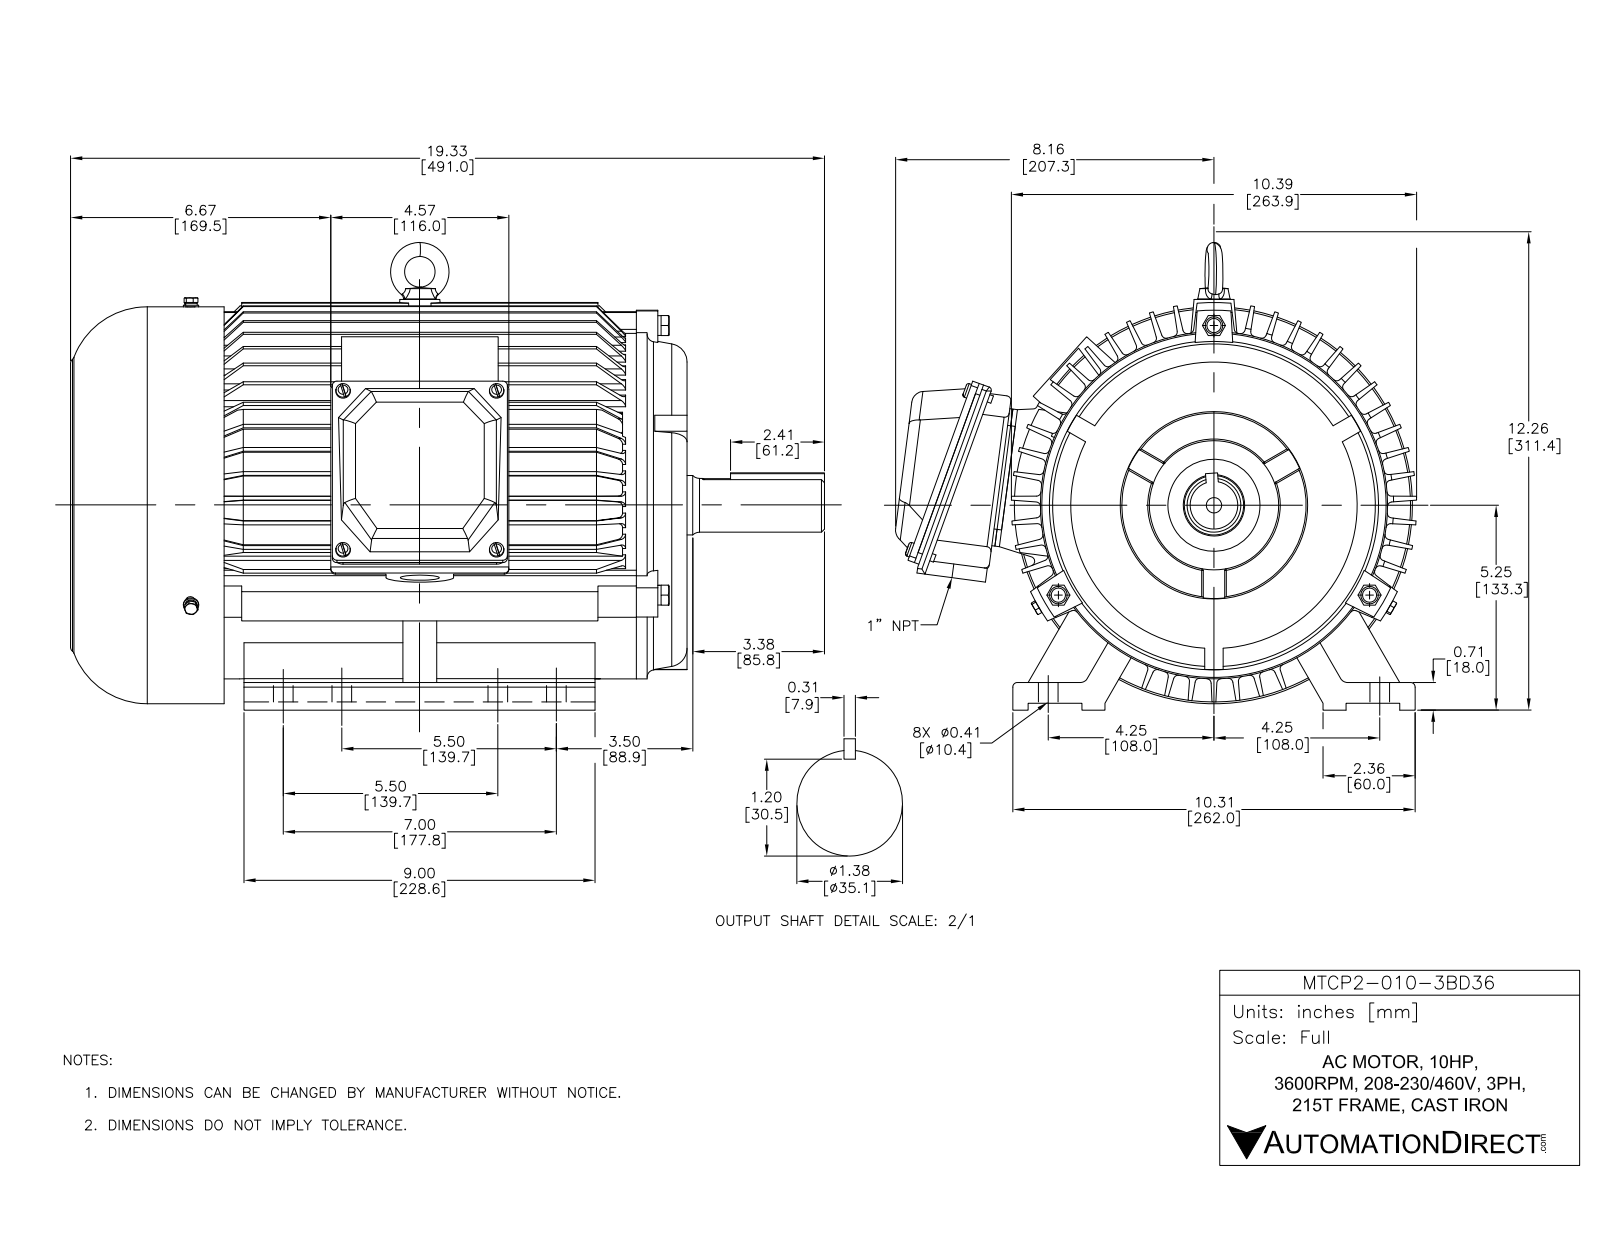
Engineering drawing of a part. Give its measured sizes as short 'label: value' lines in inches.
name: MTCP2-010-3BD18 215T
written by: SolidWorks 2017 (AUTOMOTIVE_DESIGN)
unit: in
bodies: 27 solids, 1887 faces (1094 planar, 527 cylindrical, 266 other)
size: 19.331 × 13.36 × 11.986
volume: 259.5 in³; area: 2 071 in²
holes: 8× ⌀0.228, 8× ⌀0.433, 6× ⌀0.197, 4× ⌀0.165, 4× ⌀0.236, 4× ⌀0.276, 3× ⌀0.209, 3× ⌀0.213, 3× ⌀0.315, 3× ⌀0.342, 3× ⌀0.362, 3× ⌀0.394
bosses: 7× ⌀0.197, 4× ⌀0.315, 3× ⌀0.507, 3× ⌀0.394, 3× ⌀0.283, 1× ⌀10.173, 1× ⌀10.079, 1× ⌀8.898
rounds: 104× R0.118, 17× R0.276, 12× R0.039, 8× R0.059, 8× R0.157, 8× R0.315, 6× R0.091, 6× R0.433
face distances: 0.709, 0.157, 15.699, 0.177, 0.531, 0.047, 15.746, 0.236, 15.463, 15.51
hole spacings: 3.937, 5.853, 4.331, 2.677, 1.5, 2.678, 3.785, 3.786
